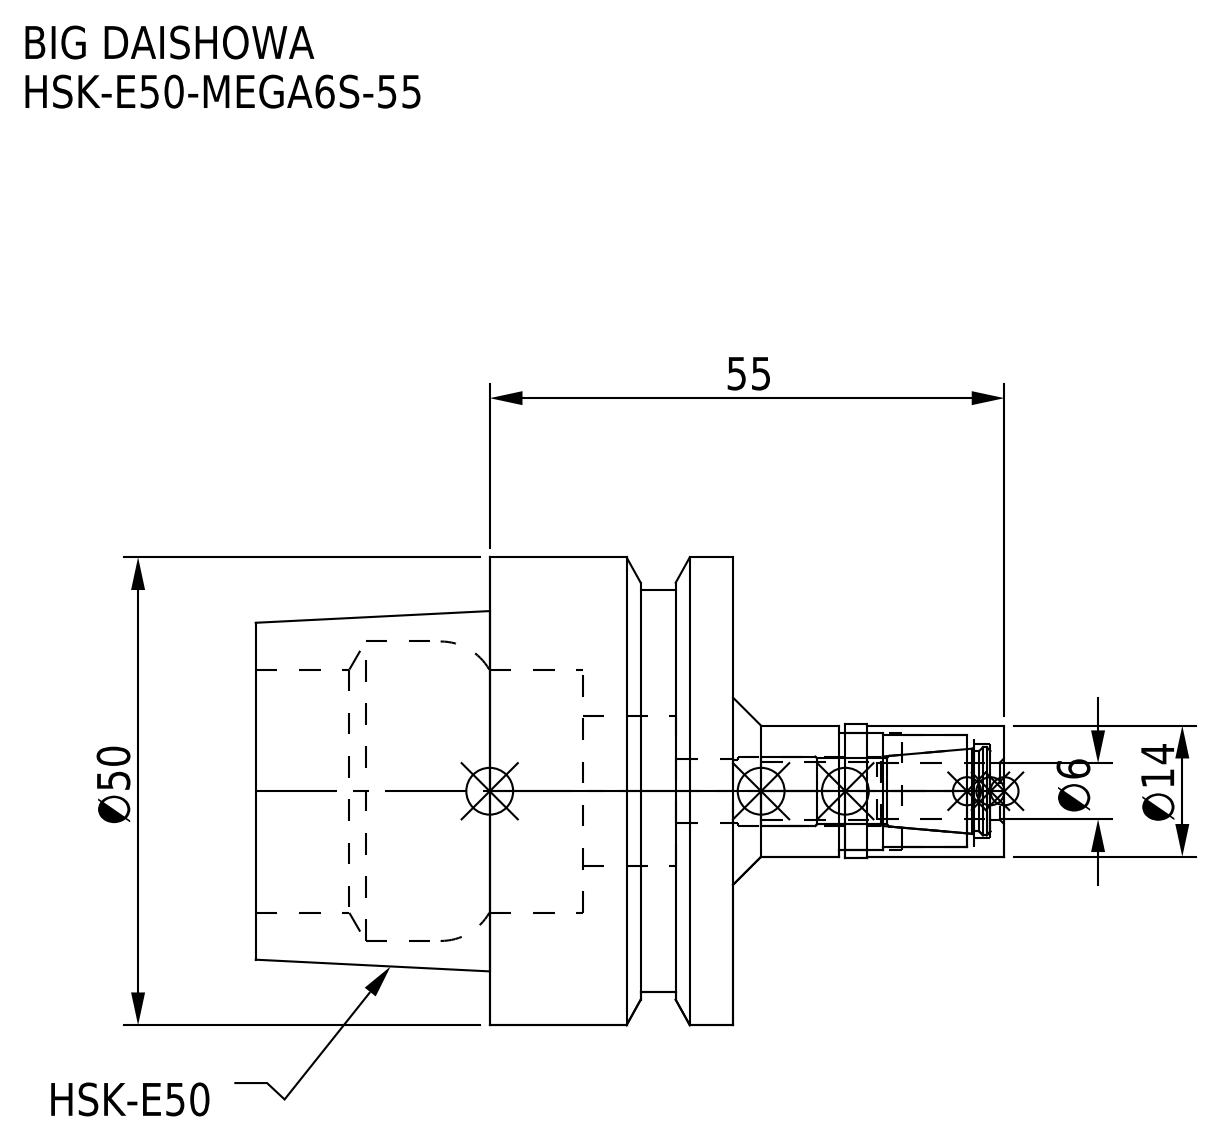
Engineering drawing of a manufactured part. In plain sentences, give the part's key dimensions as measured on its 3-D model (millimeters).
The part is named "HSK-E50-MEGA6S-55; HSK-E50-MEGA6S-55_1.stp; HSK-E50-MEGA6S-55-060-FreeParts; HSK-E50-MEGA6S-55-060.stp (+3 more)". Its 3-D file was written by "SolidWorks 2019 (CONFIG_CONTROL_DESIGN)". It is 2 solids with 74 faces: 18 planar, 40 cylindrical and 16 other. Overall it measures 80 by 50 by 50 millimeters. Its volume is 54 810 cubic millimeters and its surface area 18 442 square millimeters. Round holes: 1 of diameter 6.1, 1 of diameter 6.7, 1 of diameter 6.8, 1 of diameter 7.4, 1 of diameter 10, 1 of diameter 12, 1 of diameter 12.5, 1 of diameter 16, 1 of diameter 26, 1 of diameter 32. Round bosses or shafts: 1 of diameter 50, 1 of diameter 43, 1 of diameter 14.3, 1 of diameter 14. The main face-to-face distances are 26, 25, 51, 16.05, 9.95, 34.95, 6.05, 10, 19.95, 44.95.
